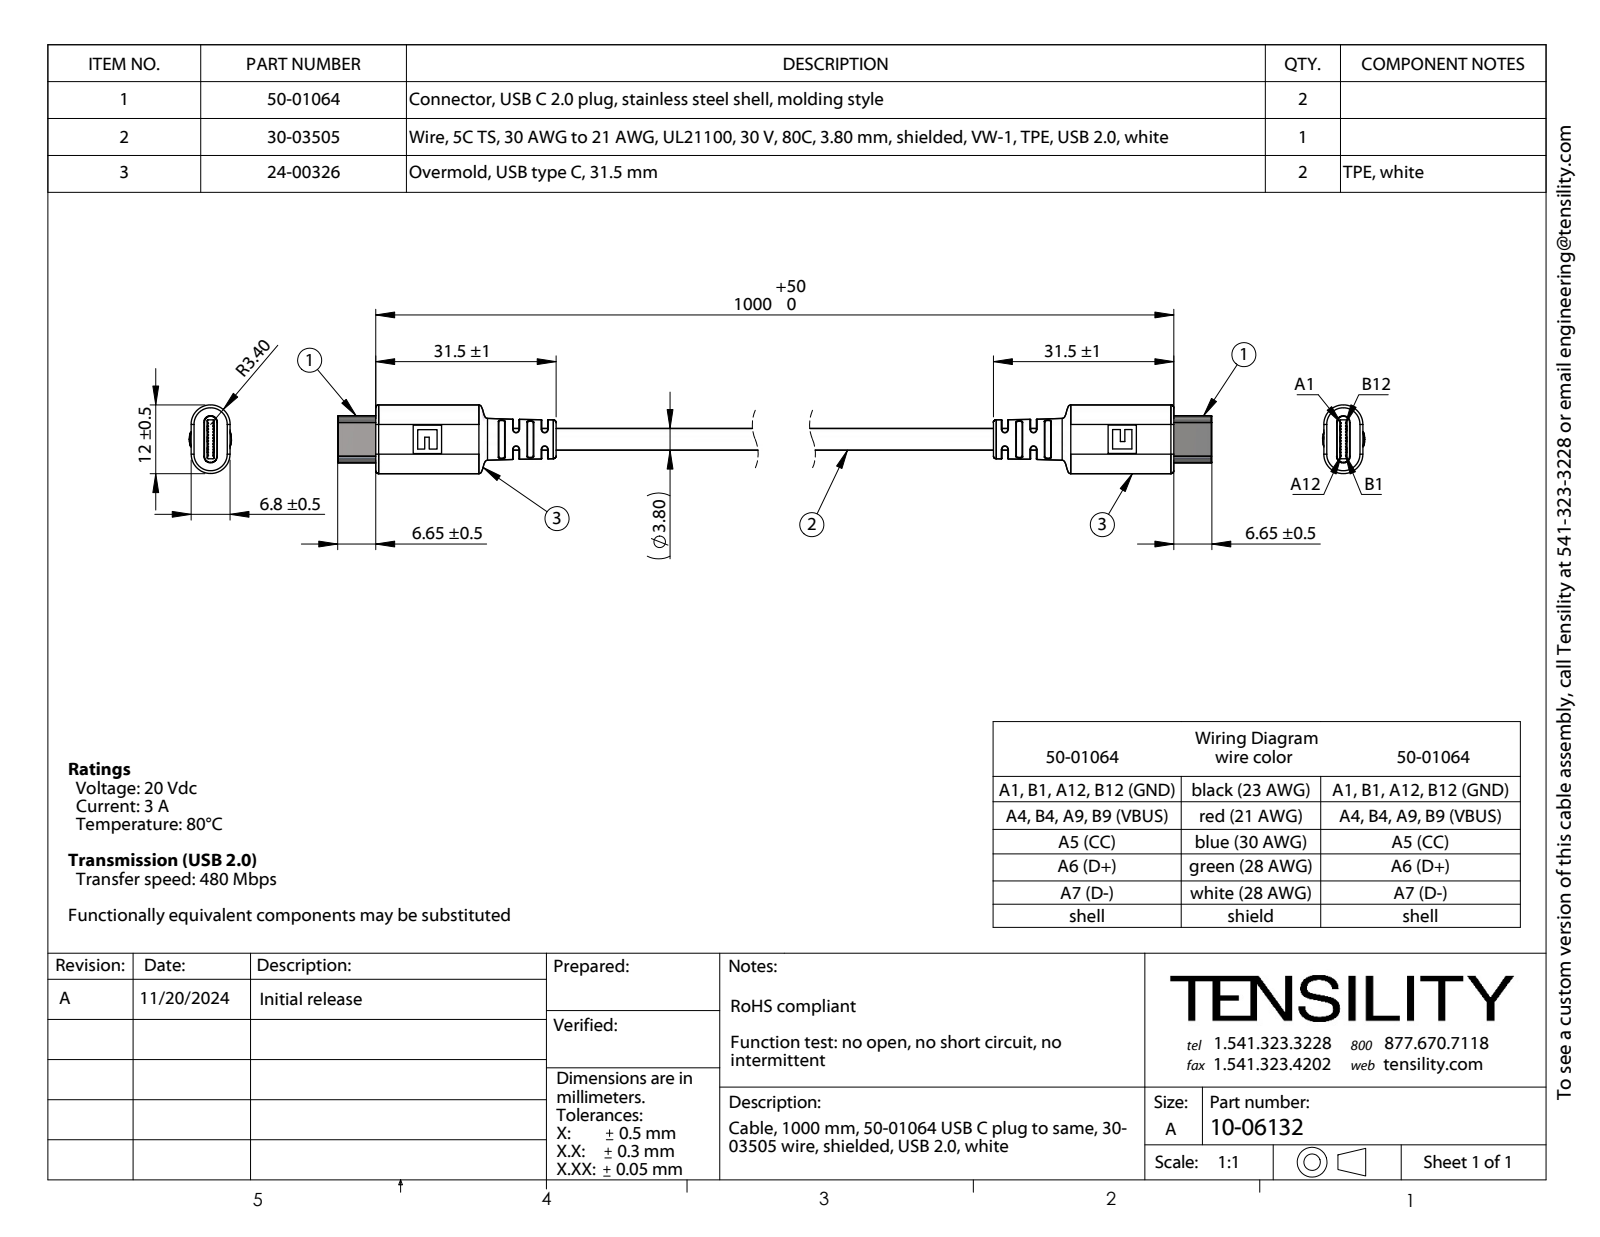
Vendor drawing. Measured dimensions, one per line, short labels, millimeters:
name: 24-00326; 50-01064_Hidden emarker; 30-03505_blunt cut; 10-06132
written by: SolidWorks 2021 (CONFIG_CONTROL_DESIGN)
unit: mm
bodies: 55 solids, 1076 faces (496 planar, 352 cylindrical, 228 other)
size: 206.3 × 12 × 7.38
volume: 5 080 mm³; area: 20 593 mm²
holes: 1× ⌀2.73, 1× ⌀2.76, 1× ⌀2.98
bosses: 2× ⌀0.83, 1× ⌀3.8, 1× ⌀2.96, 1× ⌀2.75, 1× ⌀1.2, 1× ⌀1, 1× ⌀0.55
rounds: 20× R0.5, 4× R0.1, 4× R0.15, 4× R0.25, 2× R0.6, 2× R1.18, 2× R3.4
face distances: 6.8, 2.5, 4.57, 2.23, 2.35, 0.65, 1.7, 2.22, 4.58, 1
hole spacings: 0.43, 0.33, 0.32, 0.49, 0.59, 0.44, 0.42, 1.08
